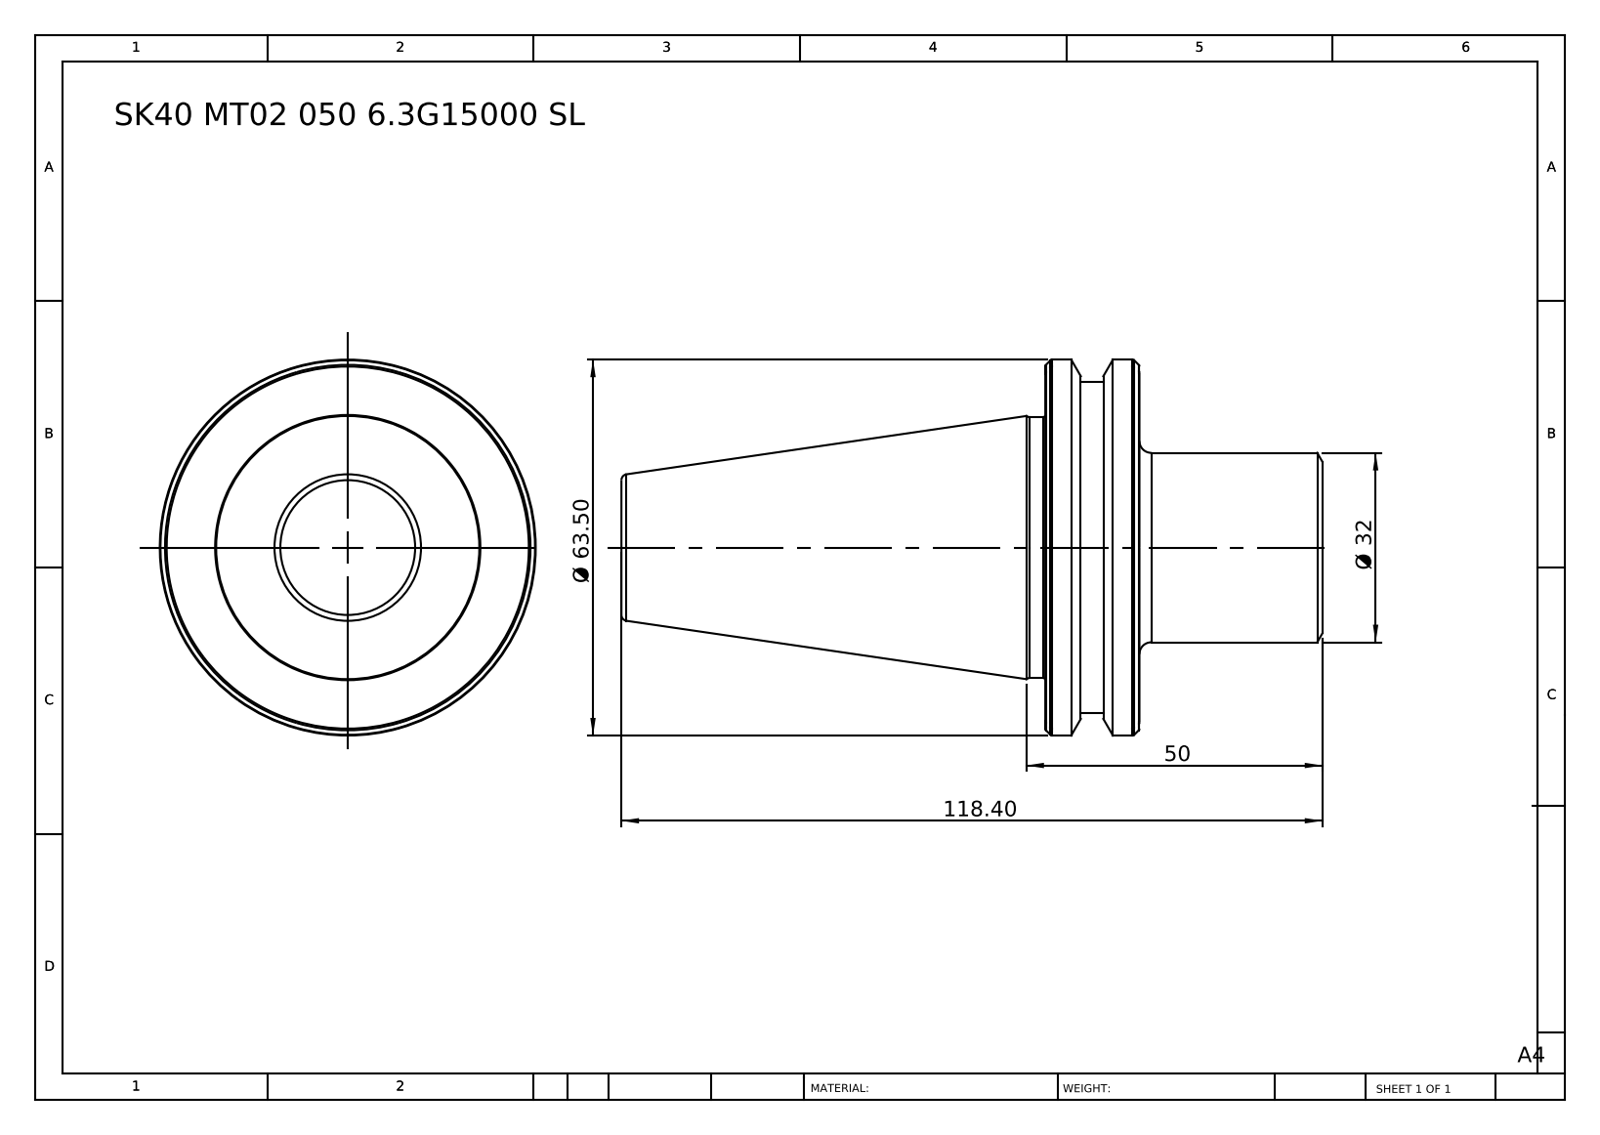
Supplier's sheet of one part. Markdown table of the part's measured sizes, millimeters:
| quantity | value |
| --- | --- |
| part name | SK 40 MT02 050 6.3G15000 SL |
| STEP written by | SolidWorks 2014 (CONFIG_CONTROL_DESIGN) |
| units | millimeters |
| bodies | 1 solid, 64 faces (6 planar, 10 cylindrical, 48 other) |
| overall size | 118.4 × 63.5 × 63.5 |
| volume | 141 980 mm³ |
| surface area | 19 892 mm² |
| round bosses / shafts (diameter × count) | 63.5 × 1, 56 × 1, 44 × 1, 32 × 1 |
| main face-to-face distances | 15.9, 30.9, 46.8, 118.4, 87.5, 71.6, 40.8, 9.9, 6, 77.6 |
